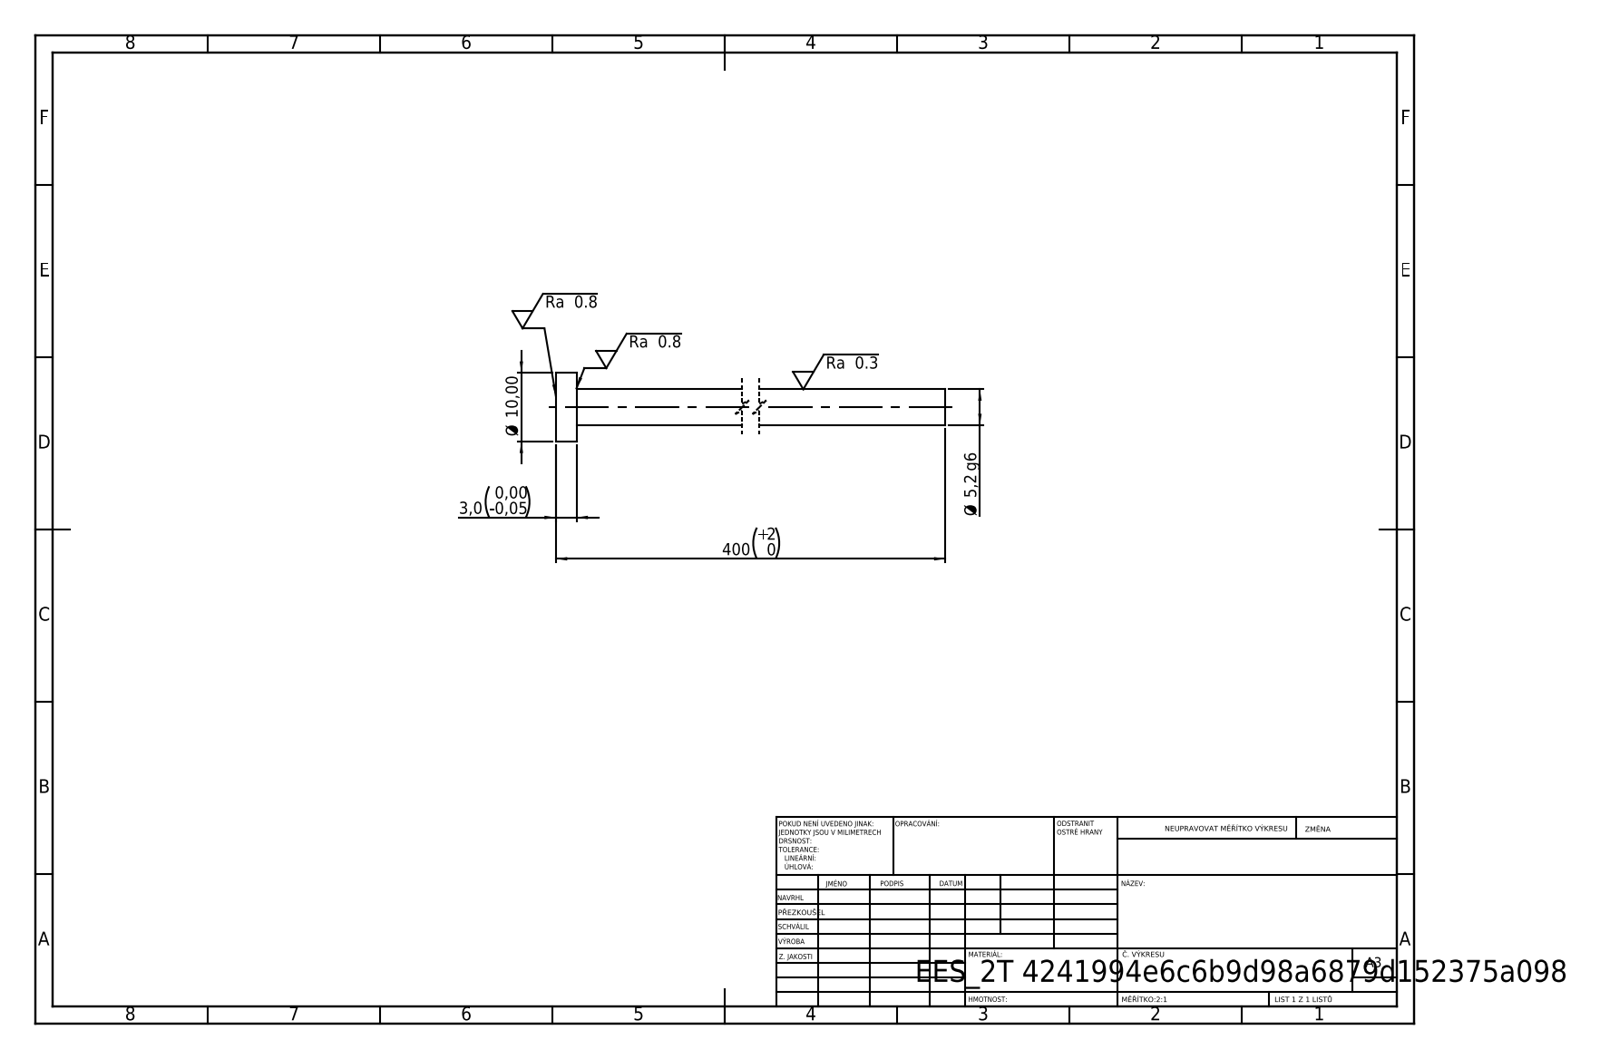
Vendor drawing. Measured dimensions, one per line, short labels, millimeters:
written by: SolidWorks 2019 (CONFIG_CONTROL_DESIGN)
unit: mm
bodies: 1 solid, 7 faces (3 planar, 4 cylindrical, 0 other)
size: 400 × 10 × 10
volume: 8 667 mm³; area: 6 737 mm²
bosses: 1× ⌀10, 1× ⌀5.2
face distances: 3, 400, 397
